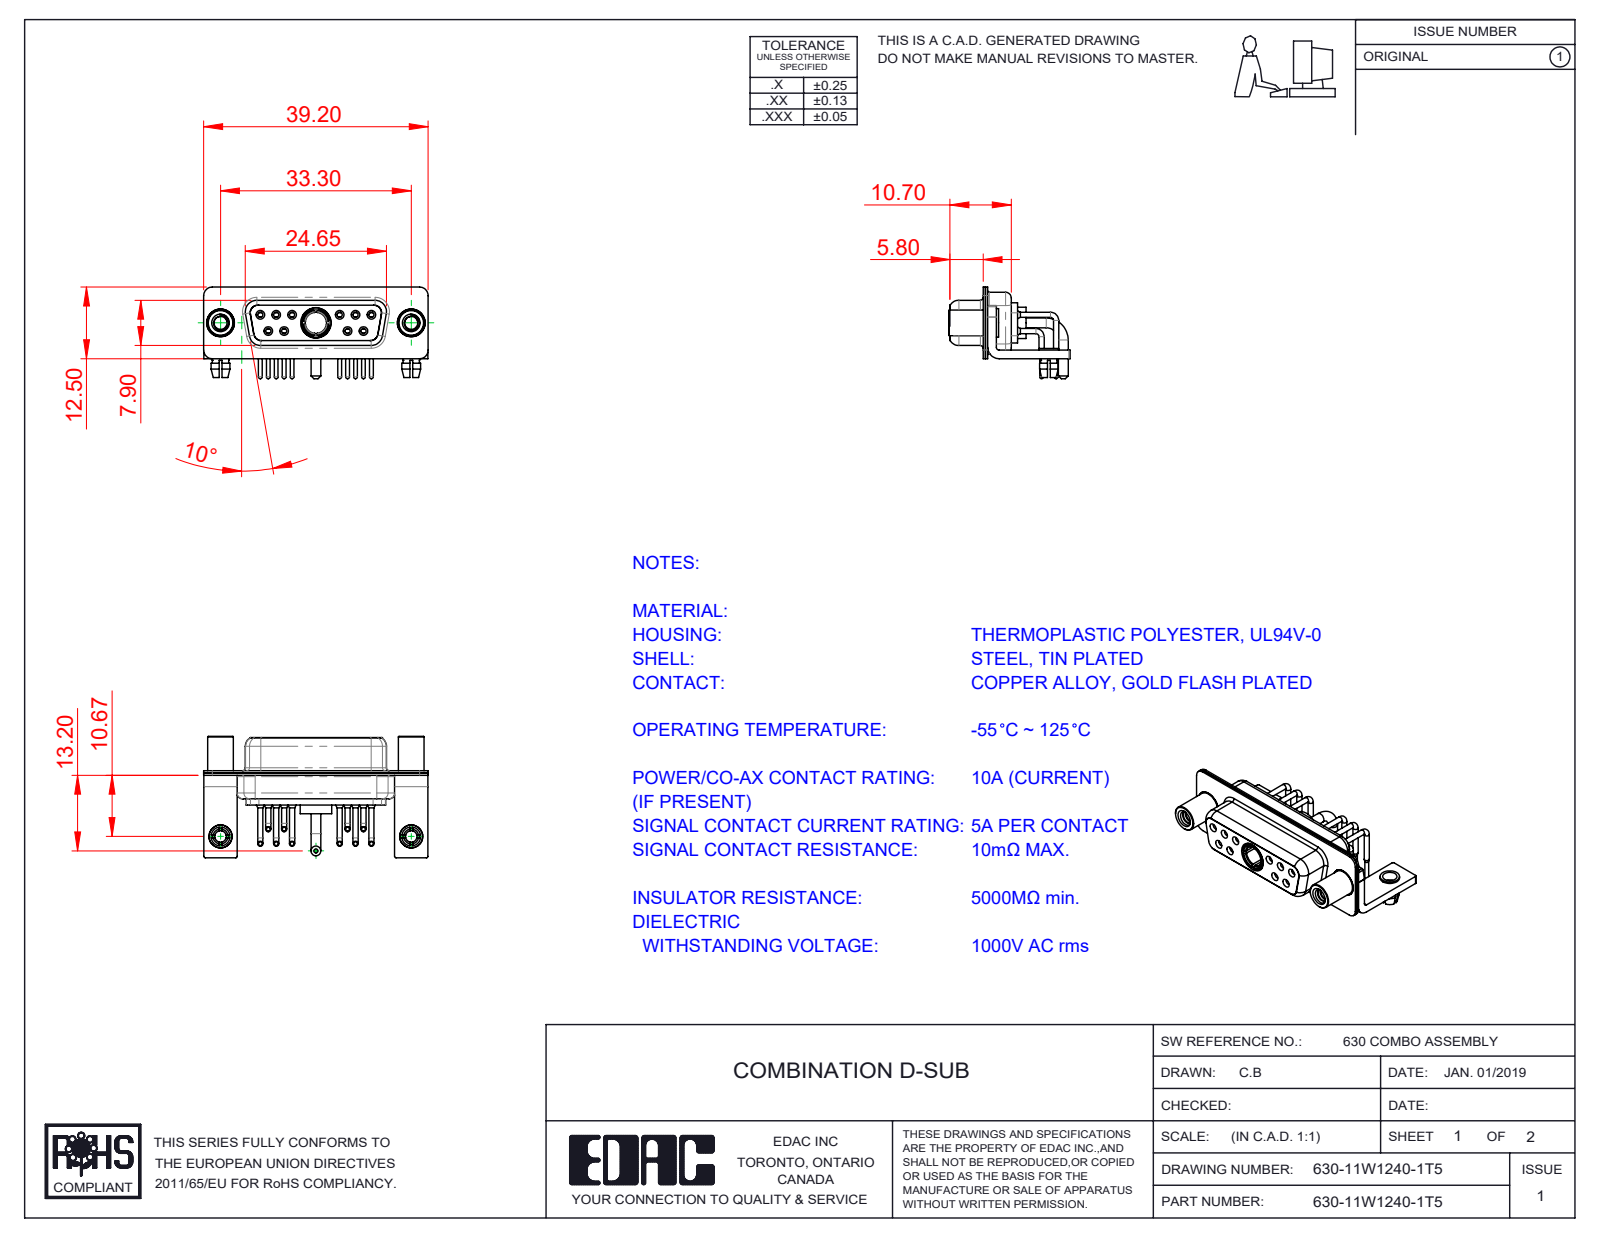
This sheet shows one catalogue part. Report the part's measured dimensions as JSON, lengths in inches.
{"part_name": "630Combo Stabilizer Bracket; 630Combo Threaded Standoff_5; 630Combo Housing_11W1; 630Combo Contact Row 1 (+6 more)", "step_written_by": "SolidWorks 2020 (CONFIG_CONTROL_DESIGN)", "units": "inches", "bodies": {"solids": 21, "faces": 1067, "planar": 316, "cylindrical": 484, "other": 267}, "overall_size": [1.543, 0.835, 0.63], "volume_in3": 0.184, "surface_area_in2": 11.39, "round_holes": [[0.079, 12], [0.035, 10], [0.043, 10], [0.059, 10], [0.067, 6], [0.063, 4], [0.191, 3], [0.089, 2], [0.098, 2], [0.126, 2], [0.157, 2], [0.159, 2]], "round_bosses_or_shafts": [[0.035, 10], [0.026, 10], [0.063, 6], [0.197, 2], [0.195, 2], [0.189, 2], [0.177, 2], [0.157, 2]], "partial_cylinders_radius": [[0.01, 16], [0.059, 16], [0.079, 13], [0.053, 12], [0.063, 8], [0.02, 5], [0.024, 4], [0.026, 4]], "face_to_face_distances": [0.016, 0.031, 0.018, 0.055, 0.333, 0.059, 0.071, 0.35, 0.244, 0.091], "hole_center_spacings": [0.124, 0.109, 0.545, 0.436, 0.654, 0.198, 0.198, 0.218]}
